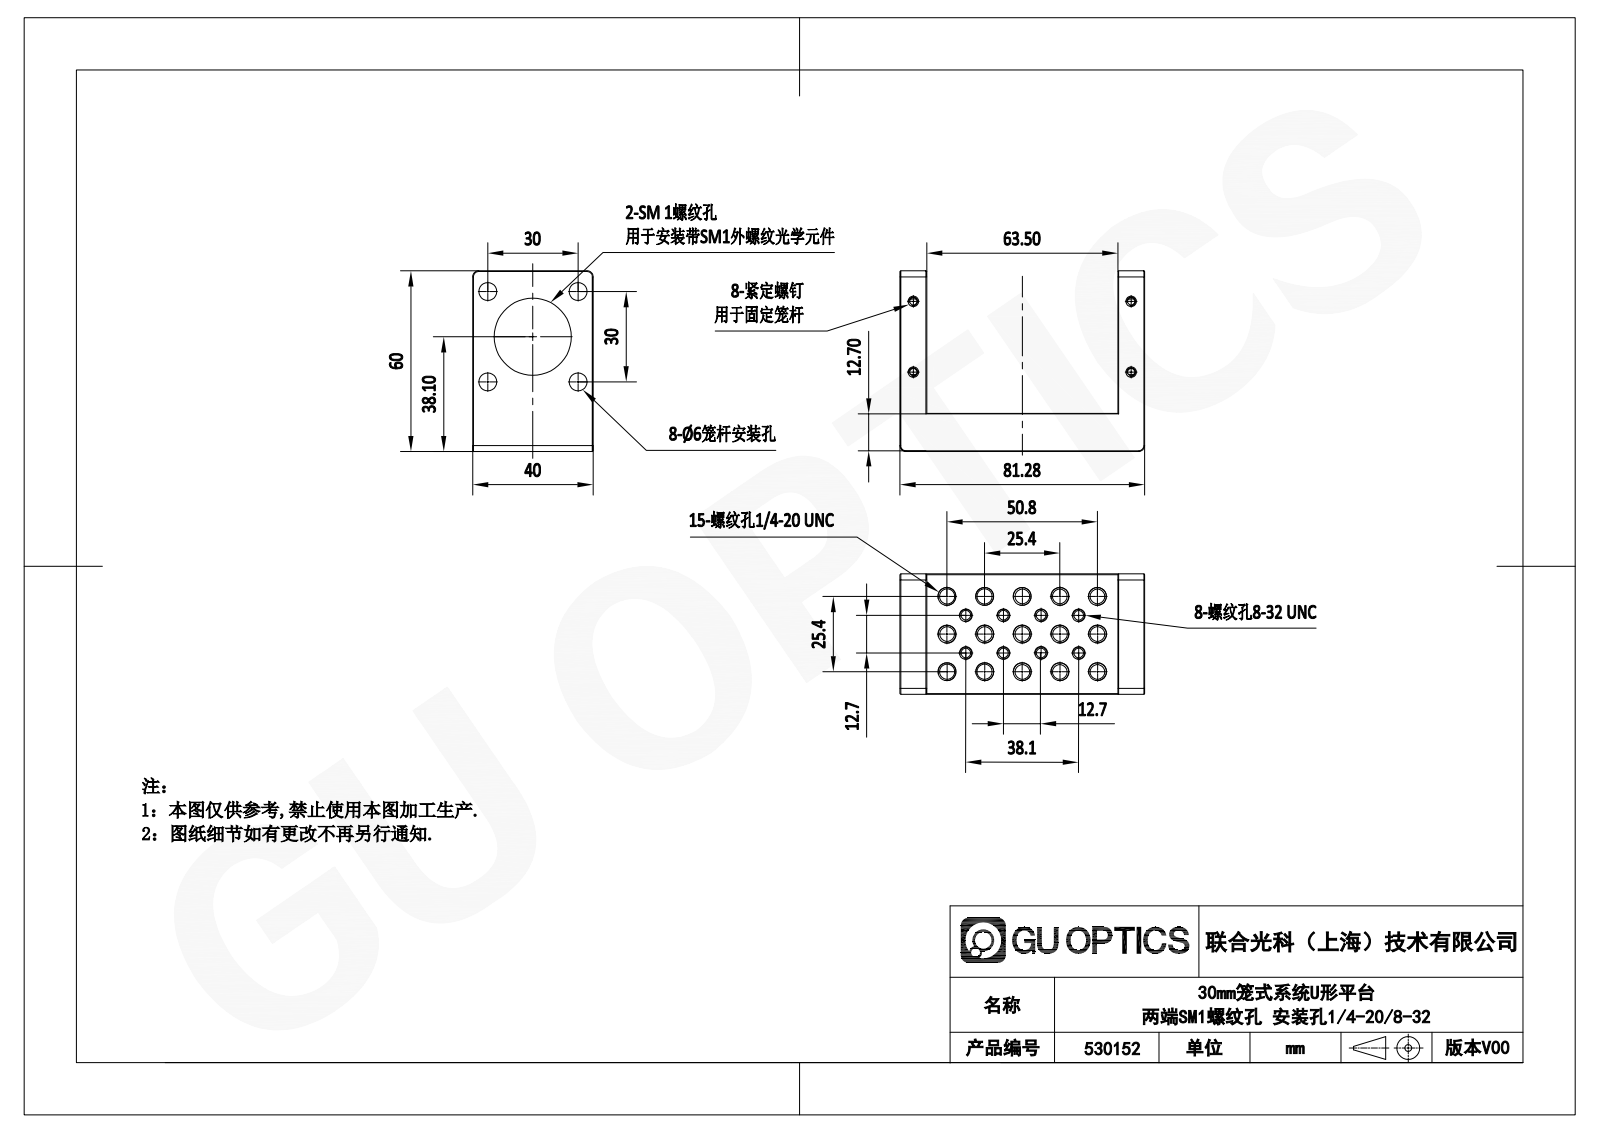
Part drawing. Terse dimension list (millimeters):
name: 530152
written by: SolidWorks 2020 (CONFIG_CONTROL_DESIGN)
unit: mm
bodies: 9 solids, 295 faces (98 planar, 55 cylindrical, 142 other)
size: 81.28 × 60 × 40
volume: 58 487 mm³; area: 22 601 mm²
holes: 15× ⌀5.11, 8× ⌀3.45, 4× ⌀2.5, 4× ⌀6, 1× ⌀25.65
bosses: 4× ⌀3
rounds: 4× R2
face distances: 8.89, 72.39, 12.7, 40, 81.28, 63.5, 60, 47.3, 51.18, 34.22
hole spacings: 20.08, 8.98, 12.7, 28.4, 17.96, 25.4, 32.38, 26.94
